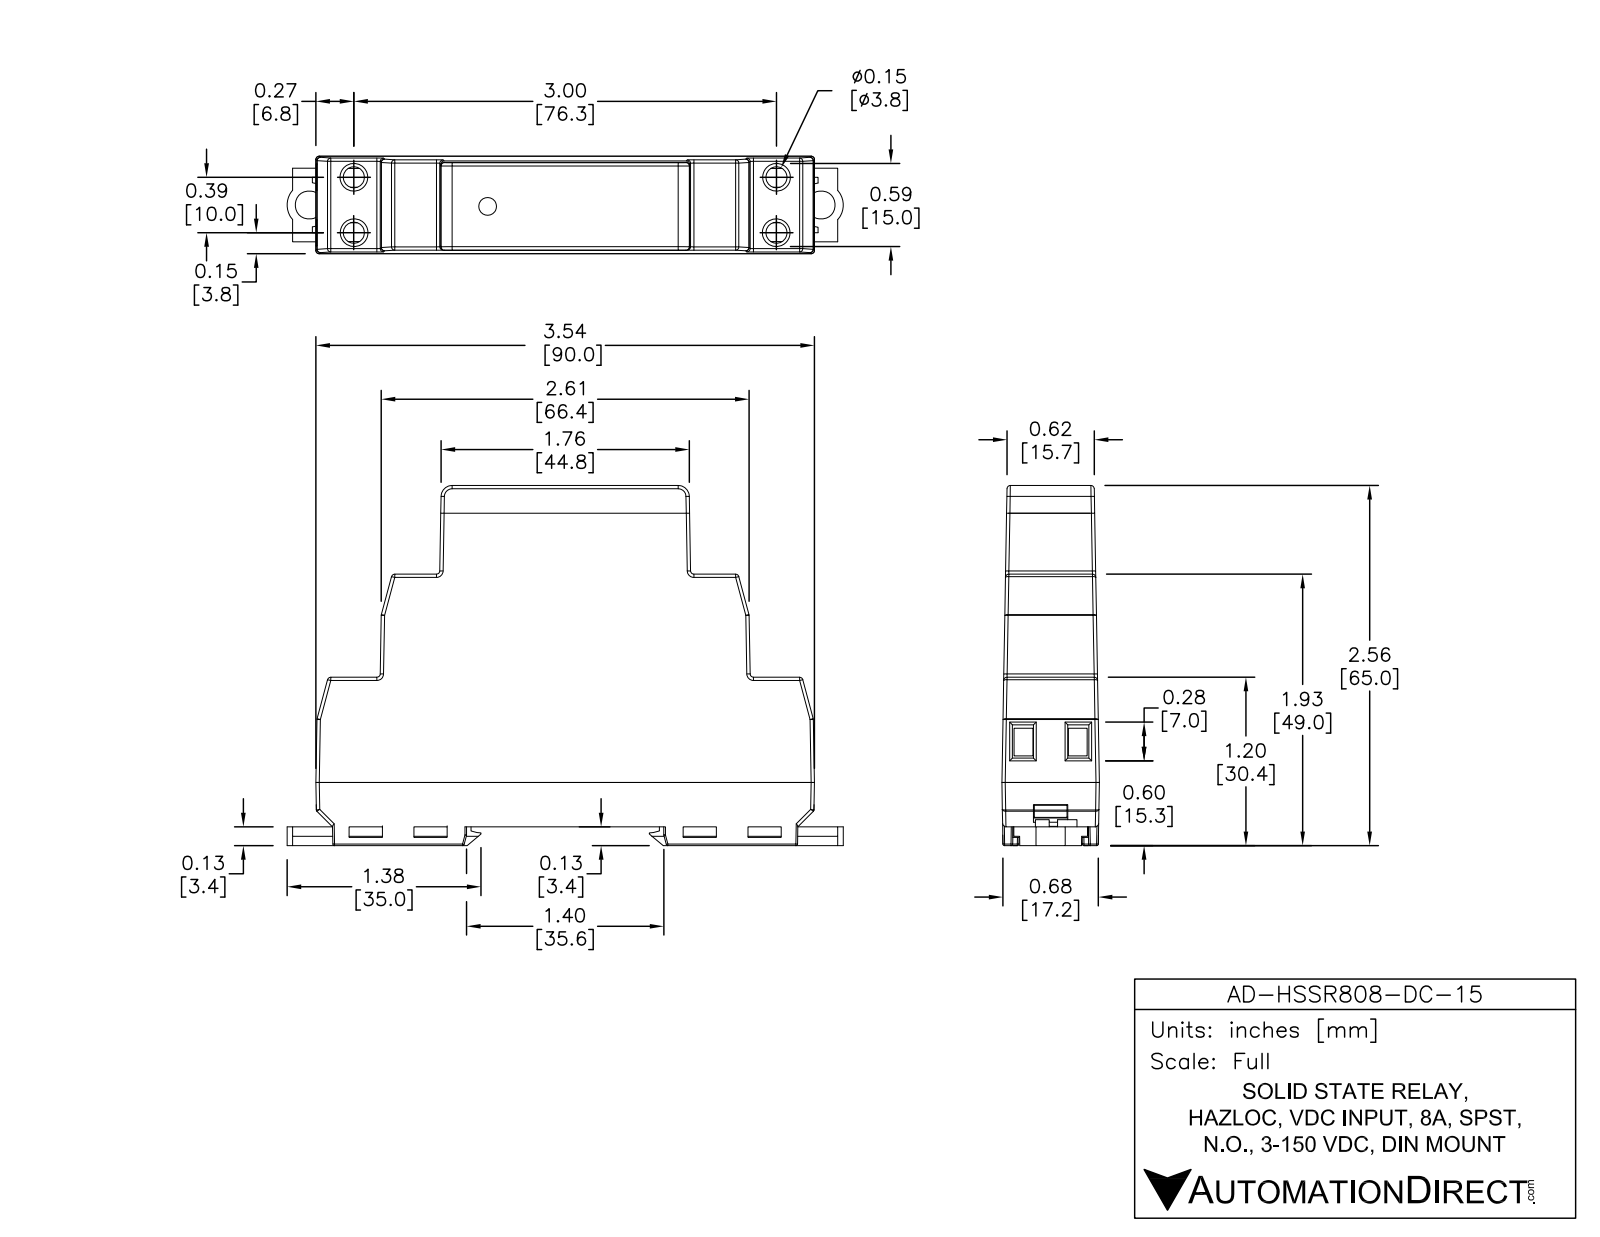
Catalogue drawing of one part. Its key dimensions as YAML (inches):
part_name: "AD-HSSR810-DC-15"
step_written_by: "SolidWorks 2013 (AUTOMOTIVE_DESIGN)"
units: inches
bodies: {solids: 35, faces: 1256, planar: 693, cylindrical: 65, other: 498}
overall_size: [3.952, 2.619, 0.692]
volume: 4.725
surface_area: 25.55
round_holes:
  - {diameter: 0.2, count: 4}
  - {diameter: 0.19, count: 2}
round_bosses_or_shafts:
  - {diameter: 0.175, count: 4}
  - {diameter: 0.1, count: 1}
partial_cylinders:
  - {radius: 0.02, count: 10}
  - {radius: 0.024, count: 10}
  - {radius: 0.012, count: 6}
  - {radius: 0.079, count: 2}
  - {radius: 0.15, count: 2}
  - {radius: 45.93, count: 2}
face_to_face_distances: [0.136, 2.559, 2.423, 0.134, 2.425, 1.929, 1.795, 1.793, 0.63, 1.197]
hole_center_spacings: [3.335, 0.379, 0.38, 0.4, 3.006, 3.033, 3.652]
